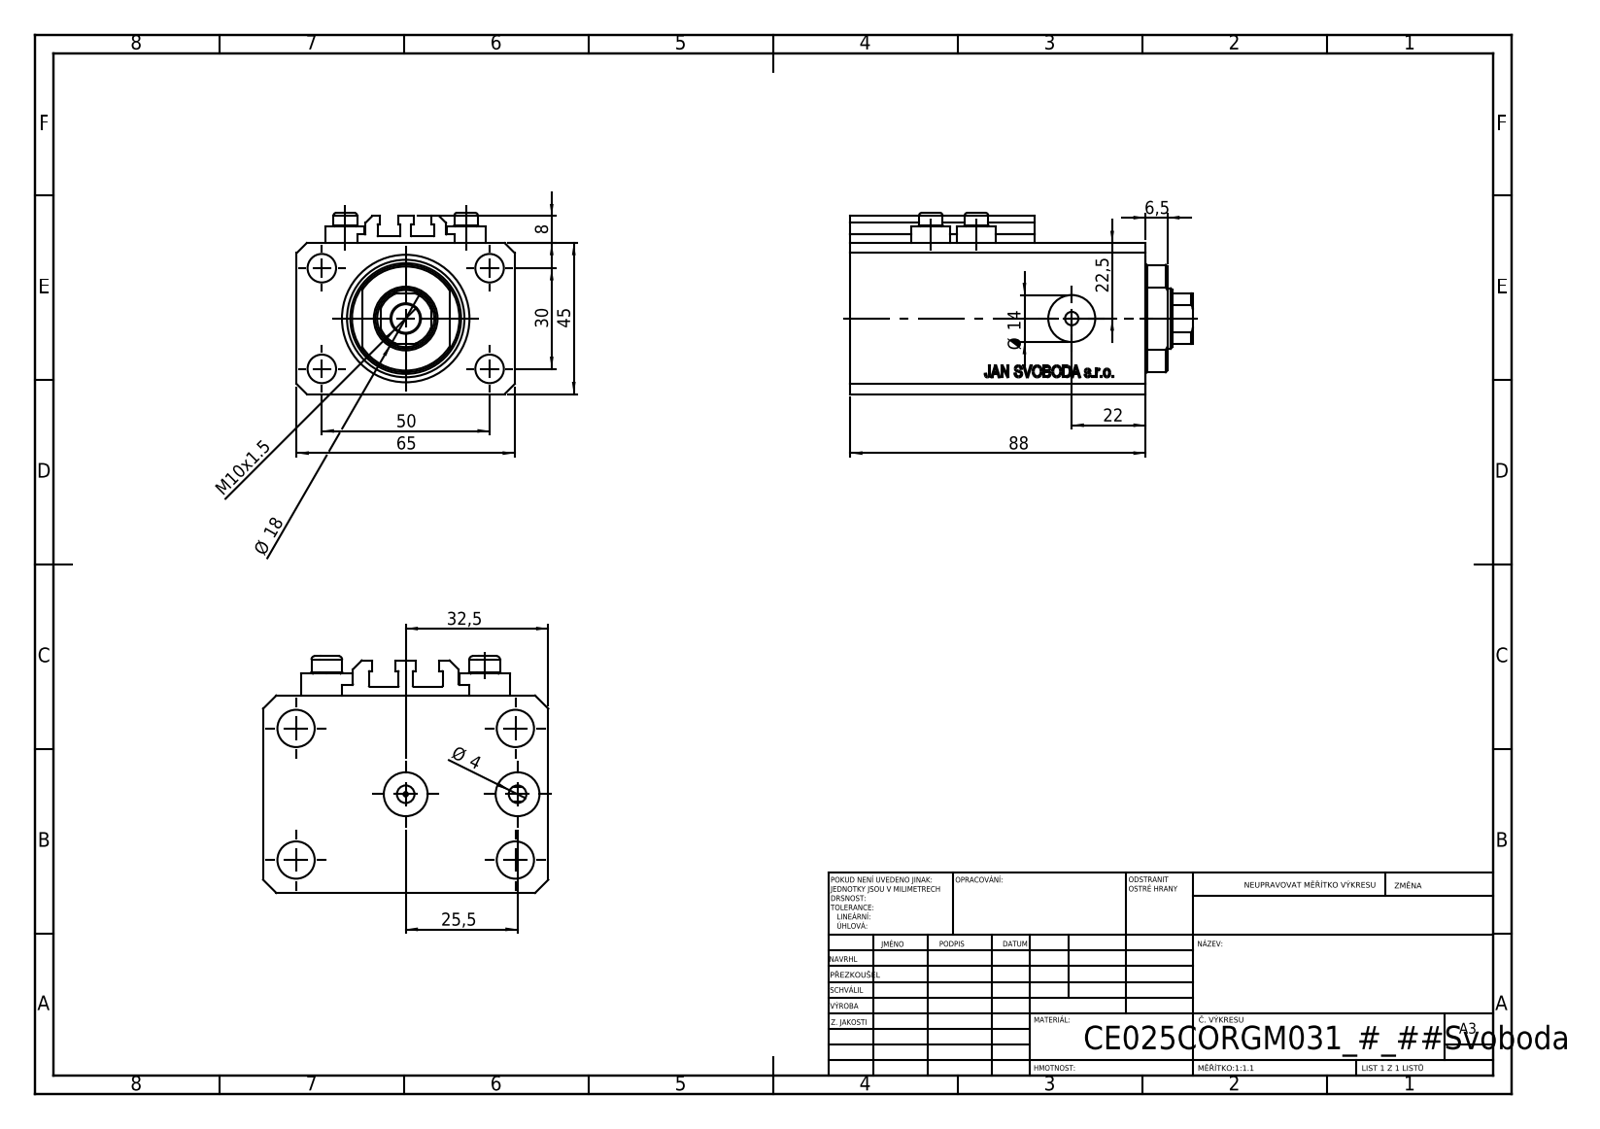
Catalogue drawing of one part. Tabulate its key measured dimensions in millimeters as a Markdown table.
| quantity | value |
| --- | --- |
| part name | V250CE_C_VCP; V250CE_C_Body; ALLEN BOLT V250CE; V250CE_VC_C |
| STEP written by | SolidWorks 2019 (CONFIG_CONTROL_DESIGN) |
| units | millimeters |
| bodies | 8 solids, 1041 faces (505 planar, 90 cylindrical, 446 other) |
| overall size | 102 × 65 × 54 |
| volume | 239 760 mm³ |
| surface area | 63 800 mm² |
| round holes (diameter × count) | 4 × 8, 8.5 × 5, 10 × 2, 14 × 2, 1.25 × 1, 18 × 1, 25 × 1, 38 × 1 |
| round bosses / shafts (diameter × count) | 11.6 × 4, 7 × 4 |
| partial cylindrical surfaces (radius × count) | 0.2 × 10, 8.5 × 1, 16 × 1 |
| main face-to-face distances | 45, 65, 14, 88, 74, 47, 6.9, 67.1, 81.1, 3 |
| hole center spacings | 29.15, 13.6, 15.01, 30, 36, 38.48, 50, 52.68 |
